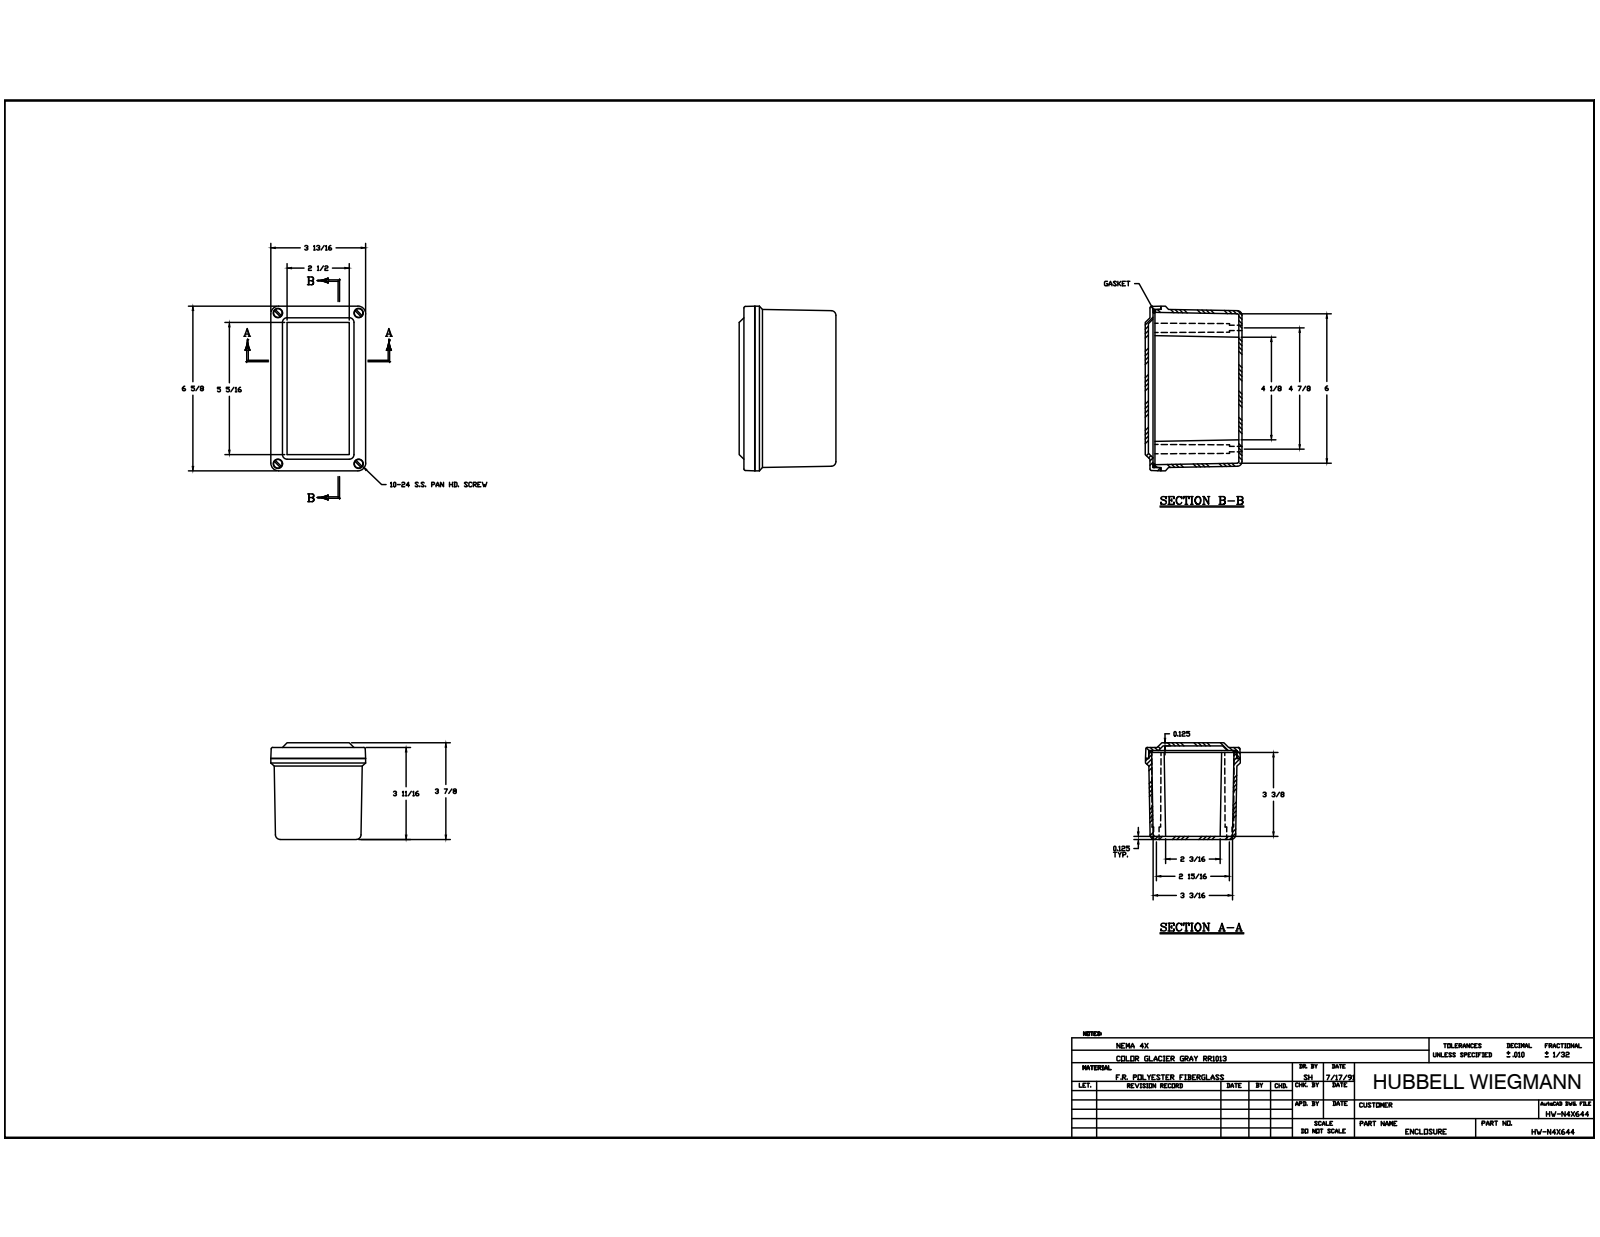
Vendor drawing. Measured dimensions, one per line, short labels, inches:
name: 10-24x0.75 DP combo screw; 10-24 X 0.4375 DP BRASS INSERT; WPCF644 BOX; WPCF644 GASKET (+3 more)
written by: Autodesk Inventor 2014 (AUTOMOTIVE_DESIGN)
unit: in
bodies: 11 solids, 379 faces (183 planar, 100 cylindrical, 96 other)
size: 6.625 × 3.875 × 3.813
volume: 20.33 in³; area: 267.6 in²
holes: 8× ⌀0.219, 4× ⌀0.145, 4× ⌀0.19, 4× ⌀0.375
bosses: 4× ⌀0.371, 4× ⌀0.218, 4× ⌀0.177
rounds: 20× R0.031, 16× R0.012, 4× R0.063, 4× R0.176, 4× R0.187, 4× R0.22, 4× R0.313, 4× R0.325
face distances: 0.125, 0.131, 3.75, 0.187, 3.563, 0.5, 3.875, 3.625, 0.063, 3.438
hole spacings: 0.614, 3.15, 5.471, 6.283, 2.938, 3.25, 4.875, 5.692
